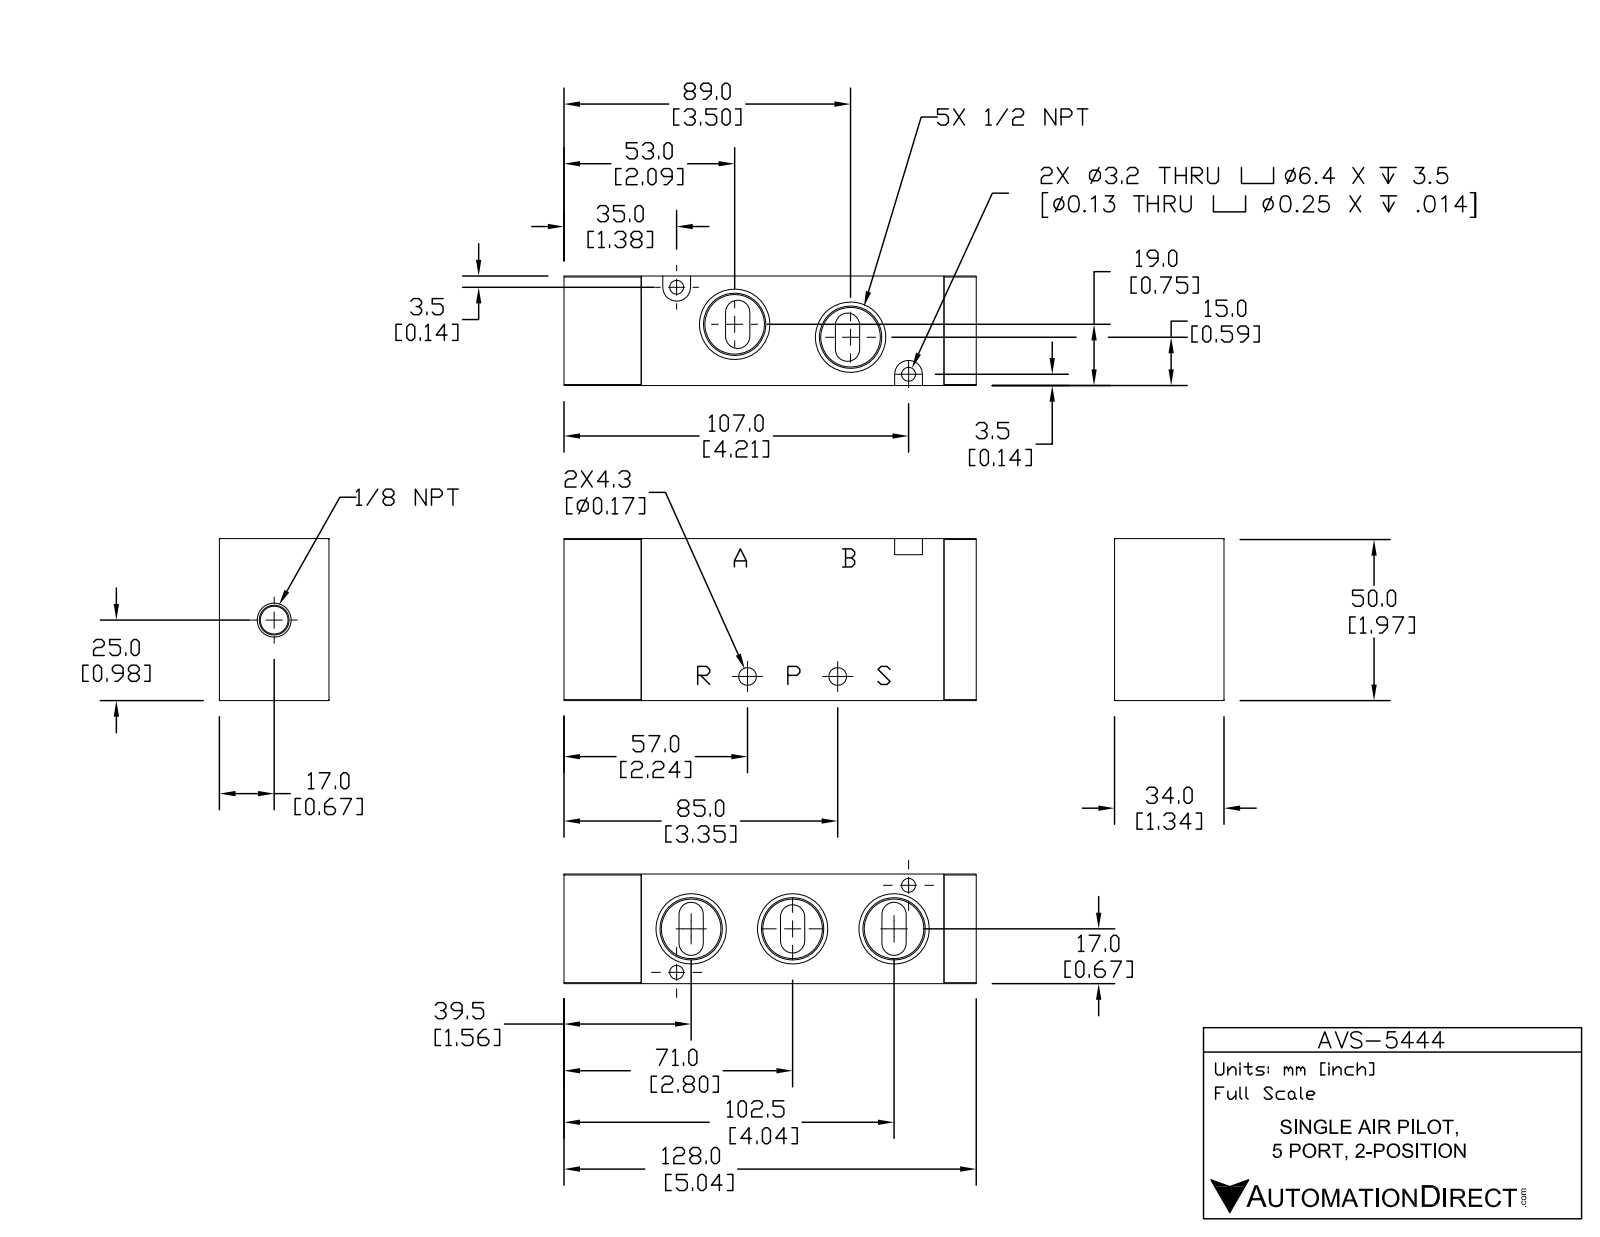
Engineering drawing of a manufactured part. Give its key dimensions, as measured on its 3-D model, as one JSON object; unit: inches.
{"part_name": "AVS-5444", "step_written_by": "SolidWorks 2015 (CONFIG_CONTROL_DESIGN)", "units": "inches", "bodies": {"solids": 3, "faces": 103, "planar": 45, "cylindrical": 34, "other": 24}, "overall_size": [5.039, 1.969, 1.339], "volume_in3": 11.57, "surface_area_in2": 61.11, "round_holes": [[0.169, 2], [0.217, 2]], "partial_cylinders_radius": [[0.148, 10], [0.012, 4], [0.169, 2]], "face_to_face_distances": [1.339, 3.701, 1.969, 0.394, 4.094, 0.945, 5.039, 4.646, 0.579, 1.389], "hole_center_spacings": [1.102, 3.028]}
